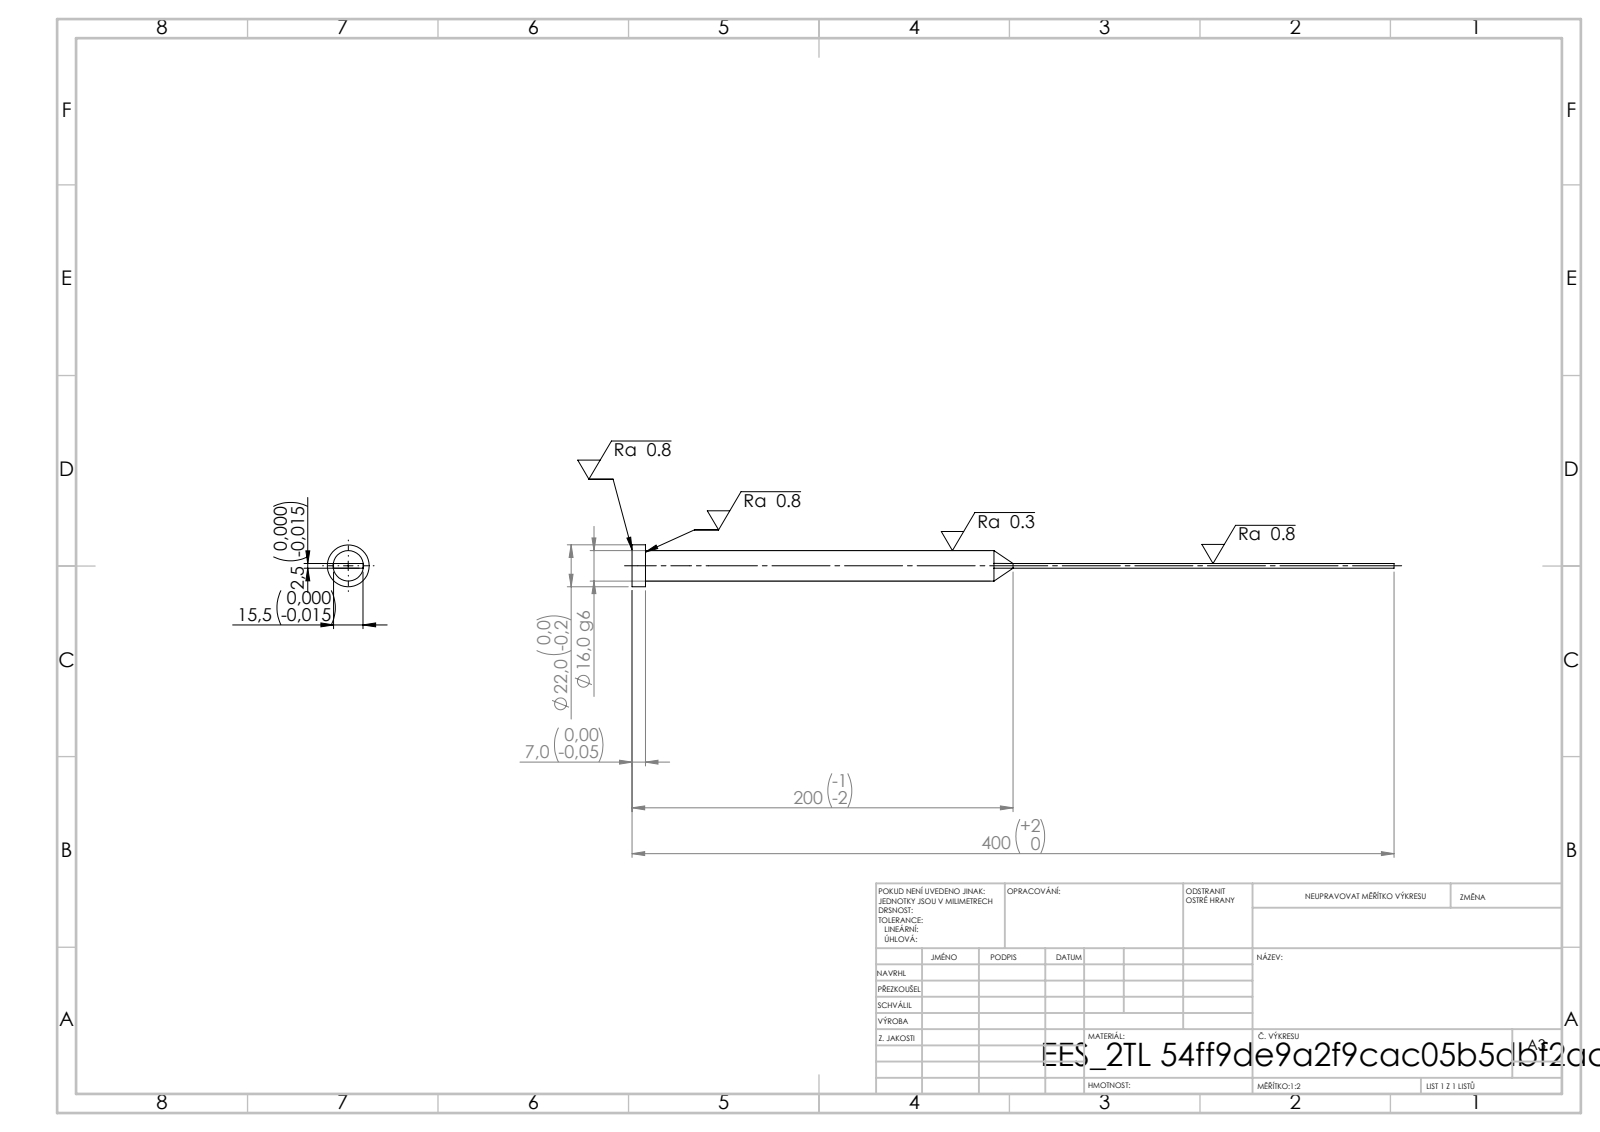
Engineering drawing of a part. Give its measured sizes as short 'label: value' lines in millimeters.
written by: SolidWorks 2019 (CONFIG_CONTROL_DESIGN)
unit: mm
bodies: 1 solid, 15 faces (7 planar, 4 cylindrical, 4 other)
size: 400 × 22 × 22
volume: 48 342 mm³; area: 17 931 mm²
bosses: 1× ⌀22, 1× ⌀16
face distances: 2.5, 15.5, 7, 400, 393
